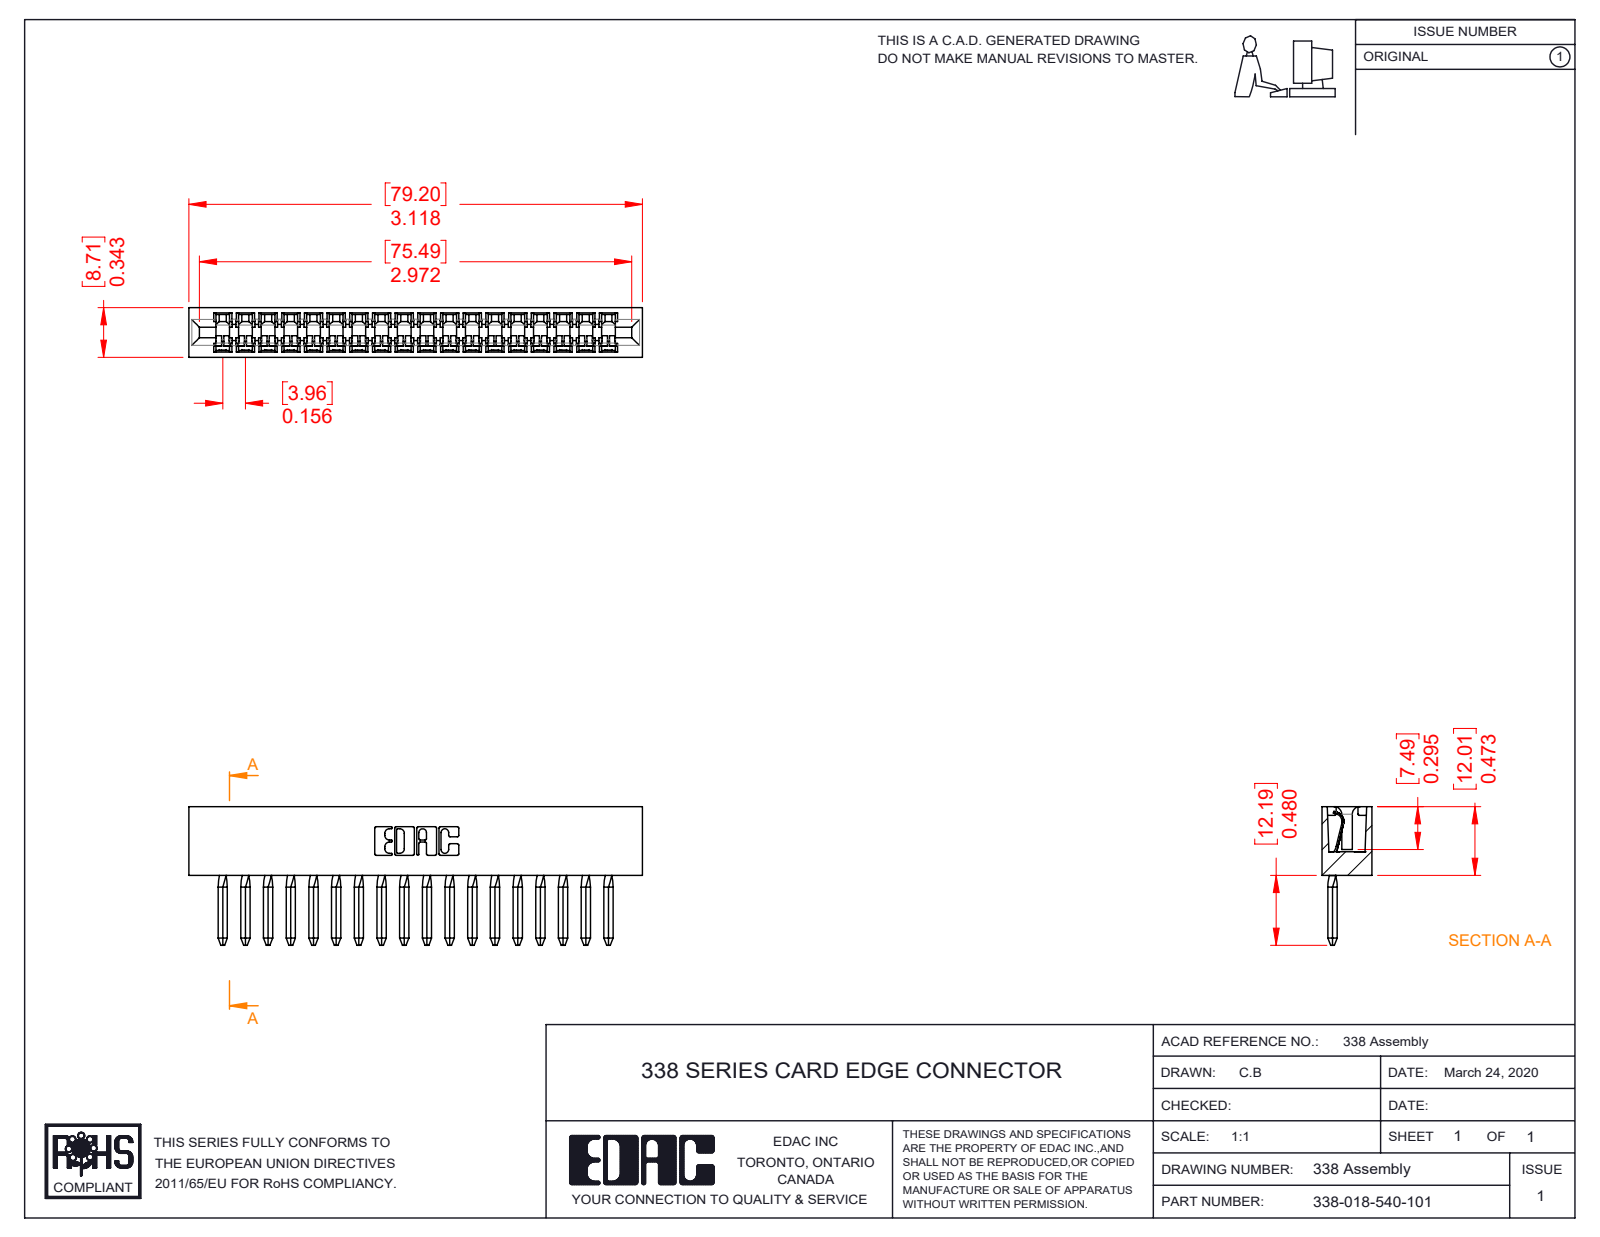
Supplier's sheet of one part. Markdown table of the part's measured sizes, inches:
| quantity | value |
| --- | --- |
| part name | 338-018-540-101; 338-290-001_540; 338-210-001_338-210-018-001 |
| STEP written by | SolidWorks 2016 (CONFIG_CONTROL_DESIGN) |
| units | inches |
| bodies | 19 solids, 1760 faces (1216 planar, 472 cylindrical, 72 other) |
| overall size | 3.118 × 0.953 × 0.343 |
| volume | 0.346 in³ |
| surface area | 14.01 in² |
| partial cylindrical surfaces (radius × count) | 0.025 × 74, 0.01 × 22, 0.008 × 18, 0.055 × 15, 0.067 × 15, 0.1 × 14, 0.007 × 6, 0.031 × 6 |
| main face-to-face distances | 0.343, 0.156, 0.624, 0.78, 0.468, 1.248, 0.312, 0.207, 0.135, 1.404 |
